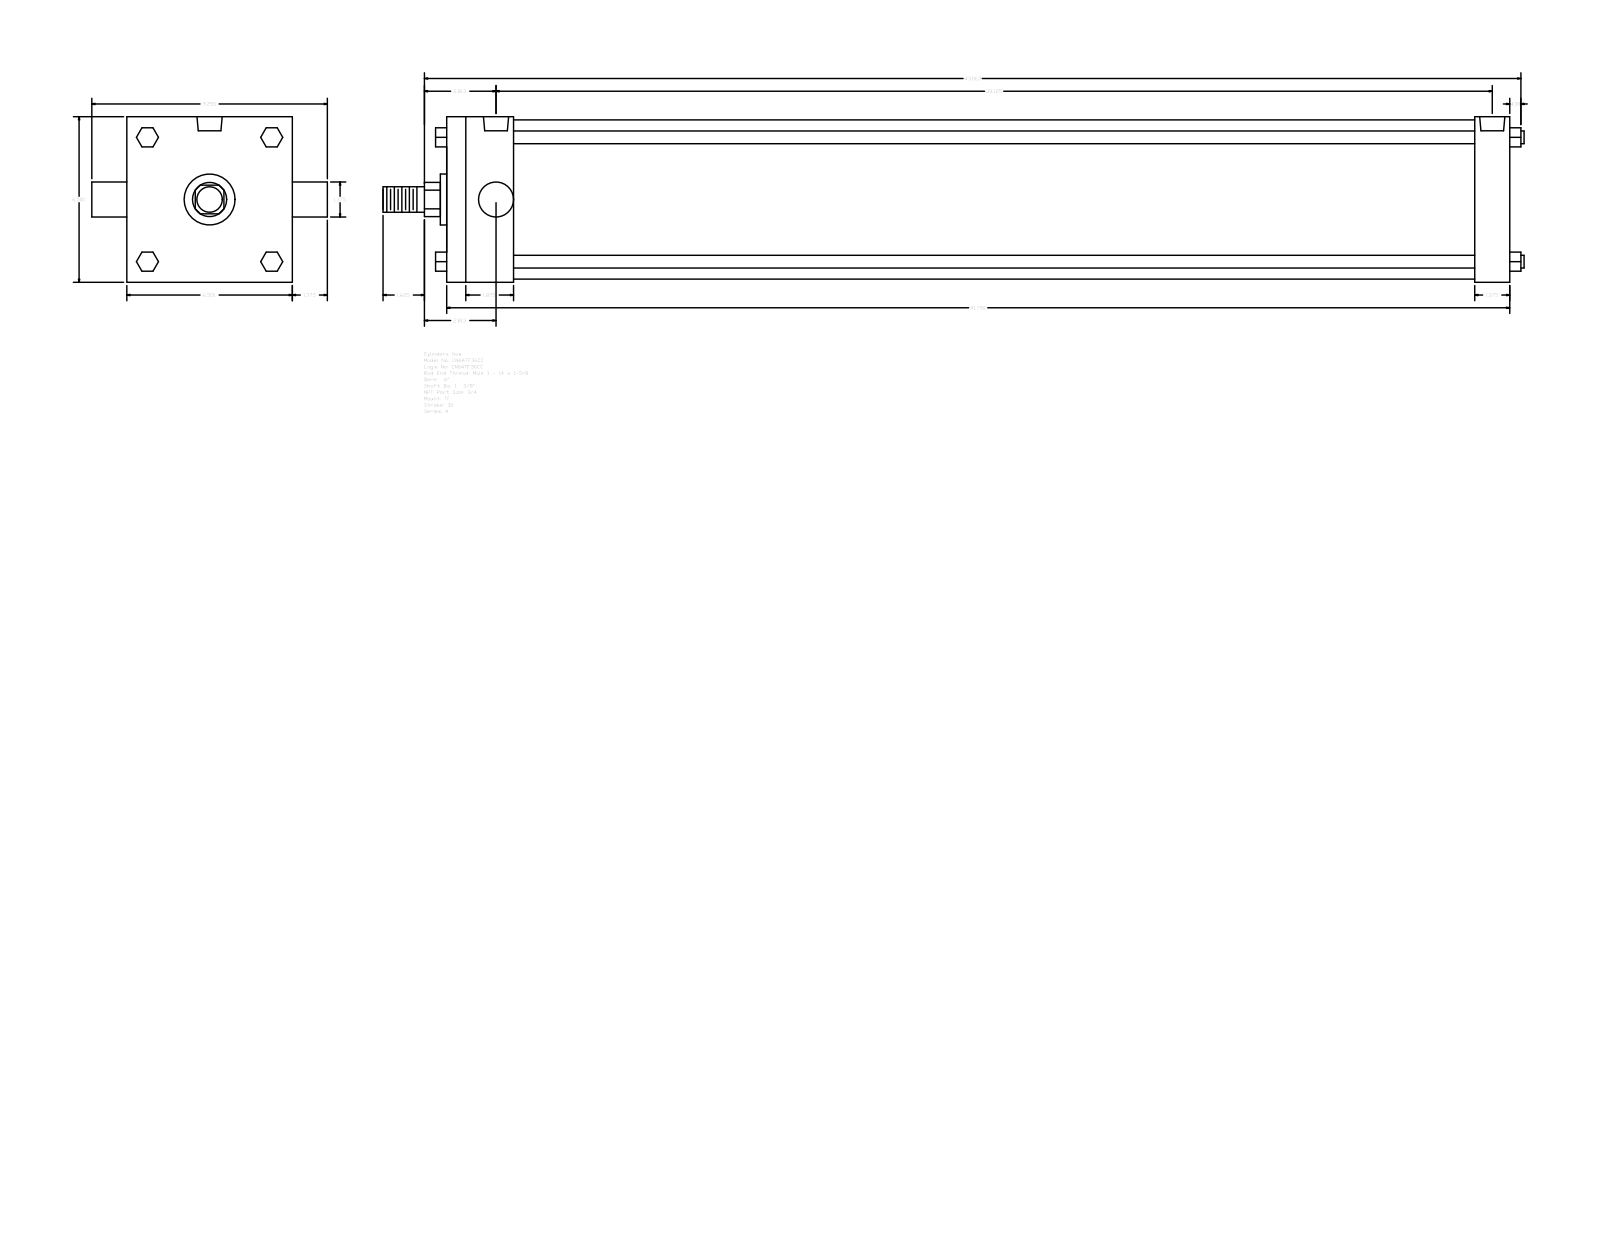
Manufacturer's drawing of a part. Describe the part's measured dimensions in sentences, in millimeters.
The part is named "A_TF__0600_1.375". Its 3-D file was written by "GSSL Pune (CONFIG_CONTROL_DESIGN)". It is 0 solids with 120 faces: 92 planar, 28 cylindrical and 0 other. Overall it measures 1138.24 by 234.95 by 165.1 millimeters. Round holes: 3 of diameter 15.08, 2 of diameter 25.12. Round bosses or shafts: 4 of diameter 12.7, 2 of diameter 34.92, 1 of diameter 158.75, 1 of diameter 50.8, 1 of diameter 25.4. Partial cylindrical surfaces (rounded edges, fillets, slot ends): 1 of radius 17.06. The main face-to-face distances are 165.1, 1060.44, 34.92, 66.67, 993.77, 1025.52, 958.85, 19.05, 61.97, 107.34. The hole center spacings are 5.56, 988.21, 982.65, 993.77.
